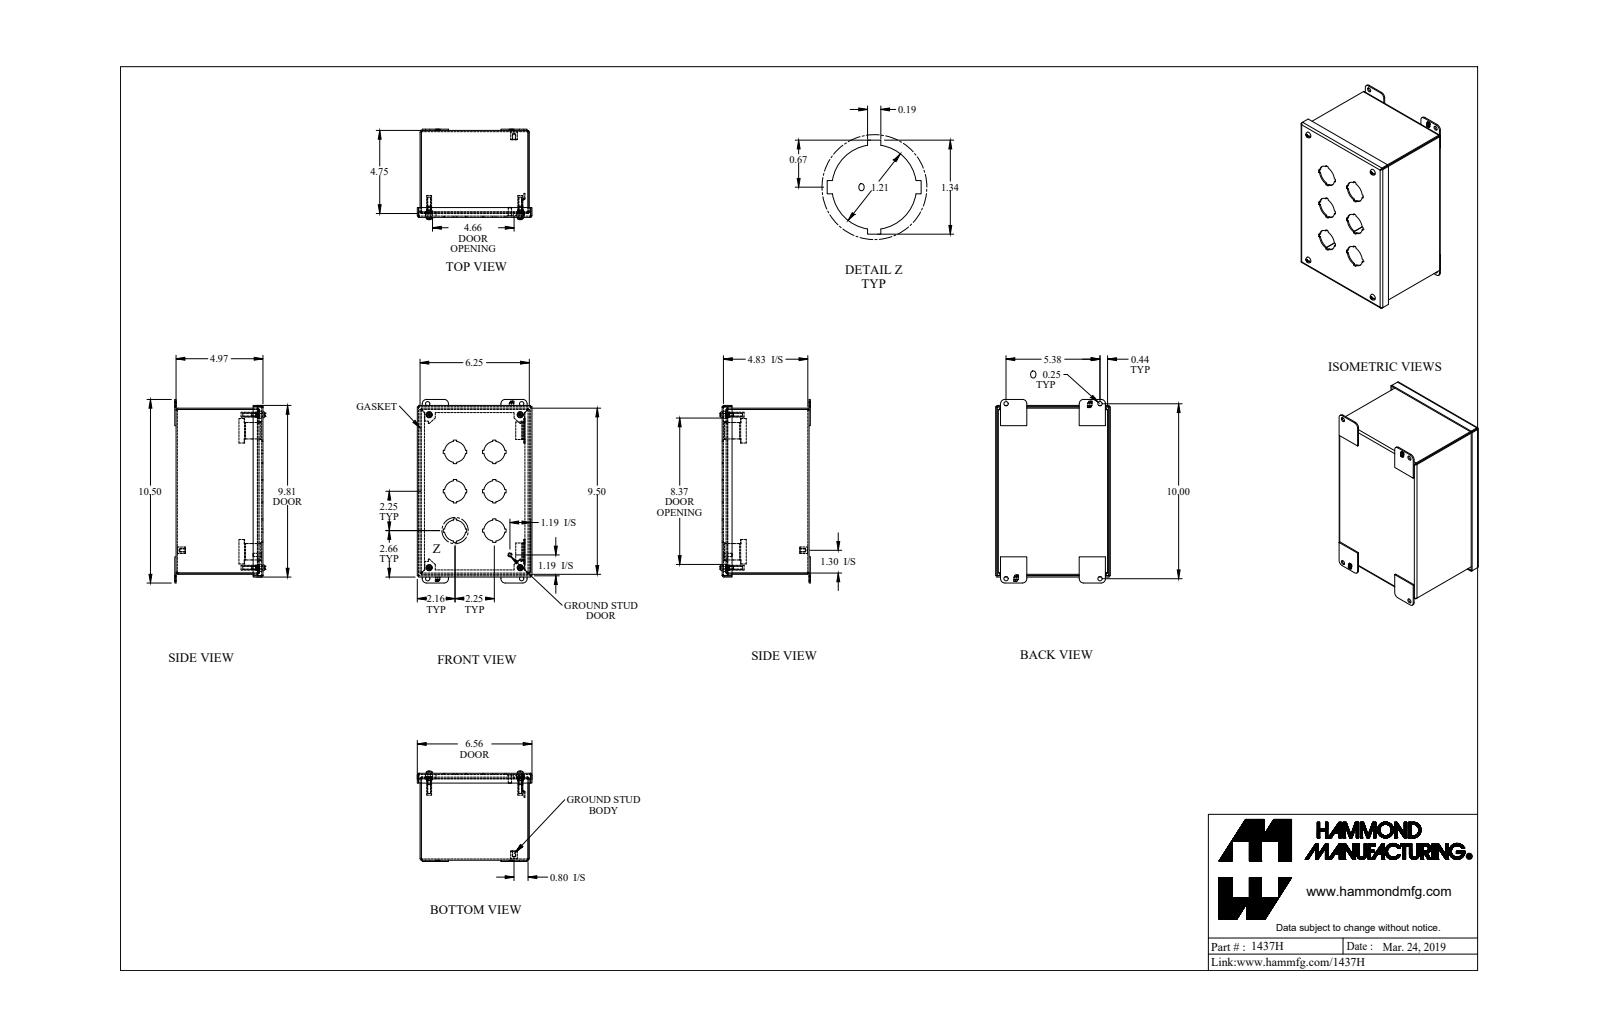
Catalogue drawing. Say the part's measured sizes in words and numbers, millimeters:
The part is named "1437H_Default". Its 3-D file was written by "SolidWorks 2019 (CONFIG_CONTROL_DESIGN)". It is 23 solids with 811 faces: 571 planar, 184 cylindrical and 56 other. Overall it measures 266.7 by 166.7 by 131.3 millimeters. Its volume is 398 700 cubic millimeters and its surface area 419 300 square millimeters. Round holes: 8 of diameter 6.4, 6 of diameter 30.7, 4 of diameter 4, 4 of diameter 10.3, 1 of diameter 4. Round bosses or shafts: 4 of diameter 9.9, 4 of diameter 7, 4 of diameter 4.8, 4 of diameter 3.8, 1 of diameter 9.5, 1 of diameter 6.4, 1 of diameter 4.8. Partial cylindrical surfaces (rounded edges, fillets, slot ends): 12 of radius 0.9, 12 of radius 2.7, 8 of radius 6.4, 4 of radius 0.7, 4 of radius 2.2, 4 of radius 4.1, 4 of radius 4.3, 2 of radius 3.2. The main face-to-face distances are 1.8, 124.5, 156.9, 126.3, 122.6, 239.5, 158.8, 155.1, 4, 237.6. The hole center spacings are 57.2, 172.4, 222.3, 238.1, 117.3, 16, 80.8, 132.3.
